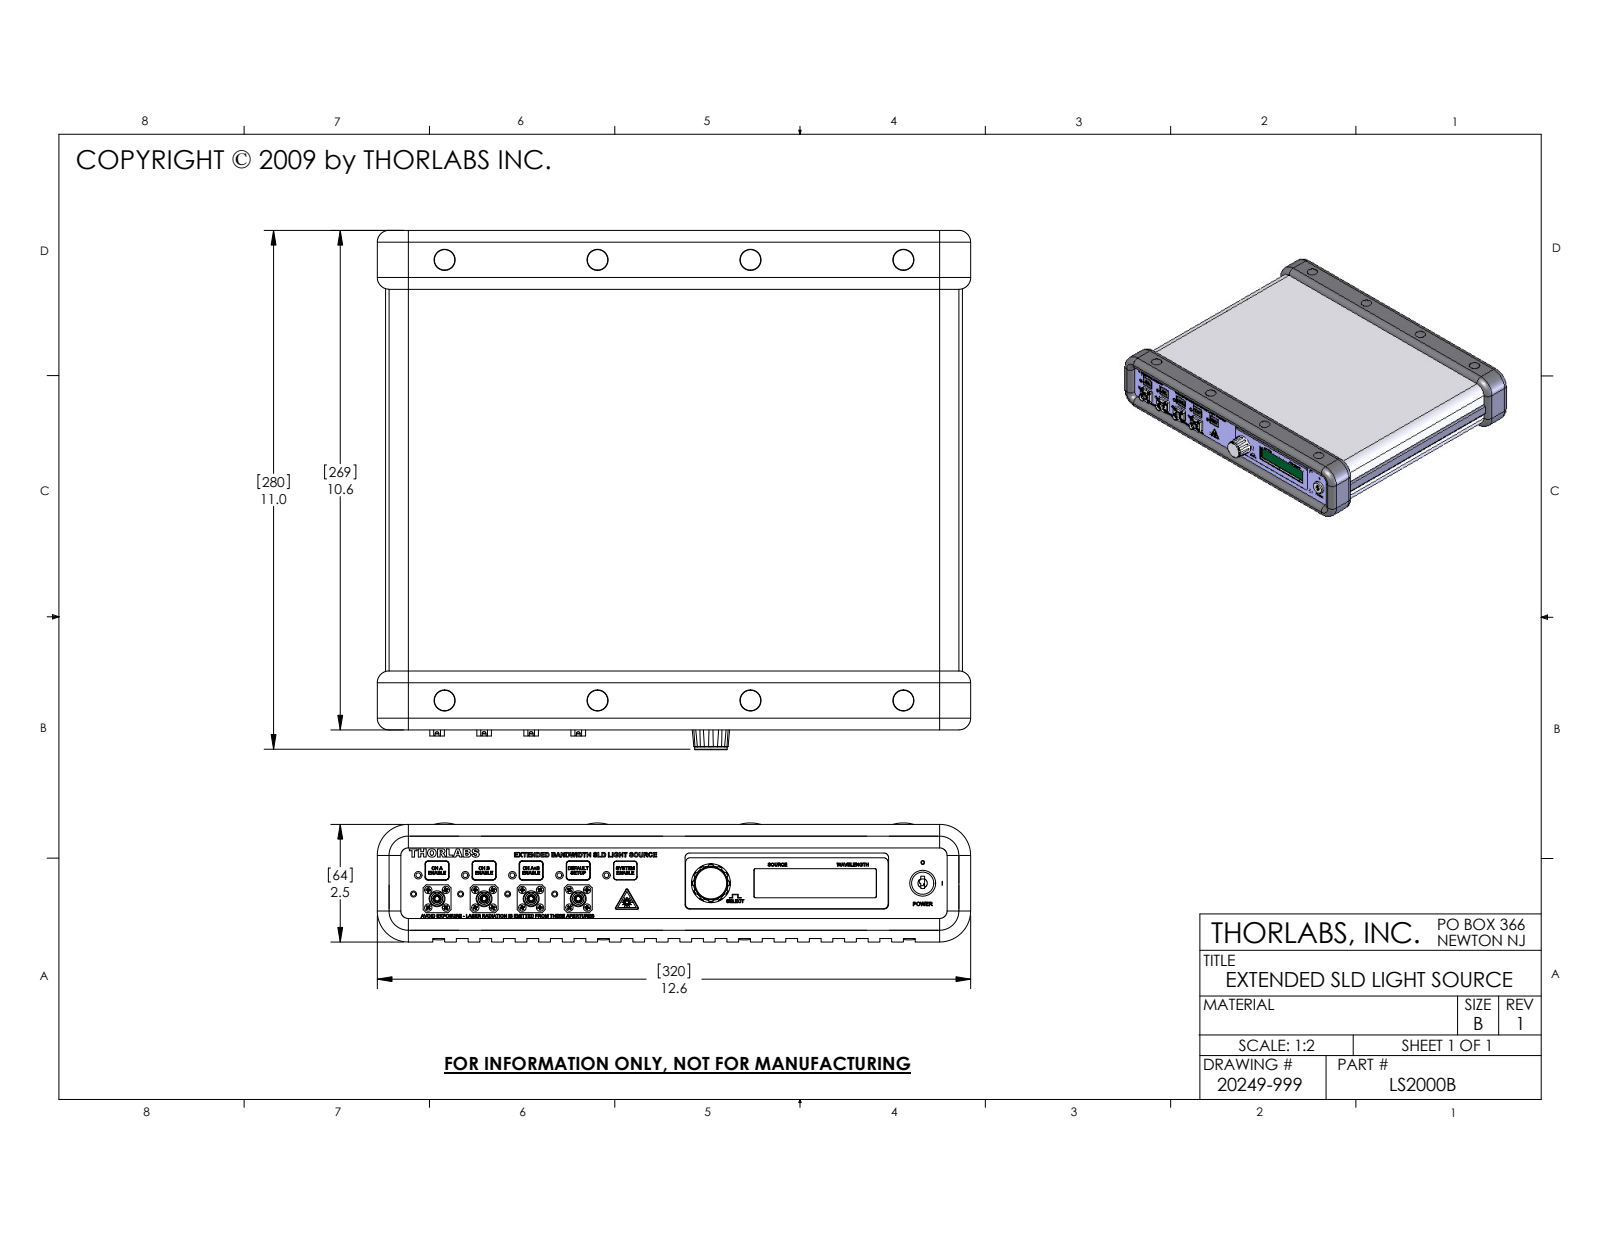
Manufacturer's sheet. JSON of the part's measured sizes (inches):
{"part_name": "20249-E0W", "step_written_by": "SolidWorks 2009 (AUTOMOTIVE_DESIGN)", "units": "inches", "bodies": {"solids": 0, "faces": 6147, "planar": 2531, "cylindrical": 2428, "other": 1188}, "overall_size": [12.61, 11.028, 2.53], "round_holes": [[0.078, 202], [0.125, 28], [0.039, 16], [0.07, 16], [0.087, 16], [0.157, 16], [0.2, 16], [0.45, 16], [0.166, 12], [0.21, 10], [0.062, 8], [0.1, 6]], "round_bosses_or_shafts": [[0.069, 16], [0.435, 10], [0.435, 6], [0.018, 6], [0.154, 5], [0.138, 5], [0.122, 5], [0.34, 4]], "partial_cylinders_radius": [[0.02, 51], [0.005, 46], [0.01, 20], [0.04, 20], [0.056, 20], [0.05, 18], [0.06, 16], [0.063, 16]], "face_to_face_distances": [0.04, 1.96, 2, 1.92, 10.04, 10, 0.25, 10.08, 10.108, 0.028], "hole_center_spacings": [0.335, 0.15, 0.212, 0.3, 0.474, 0.619, 0.45, 0.765]}
